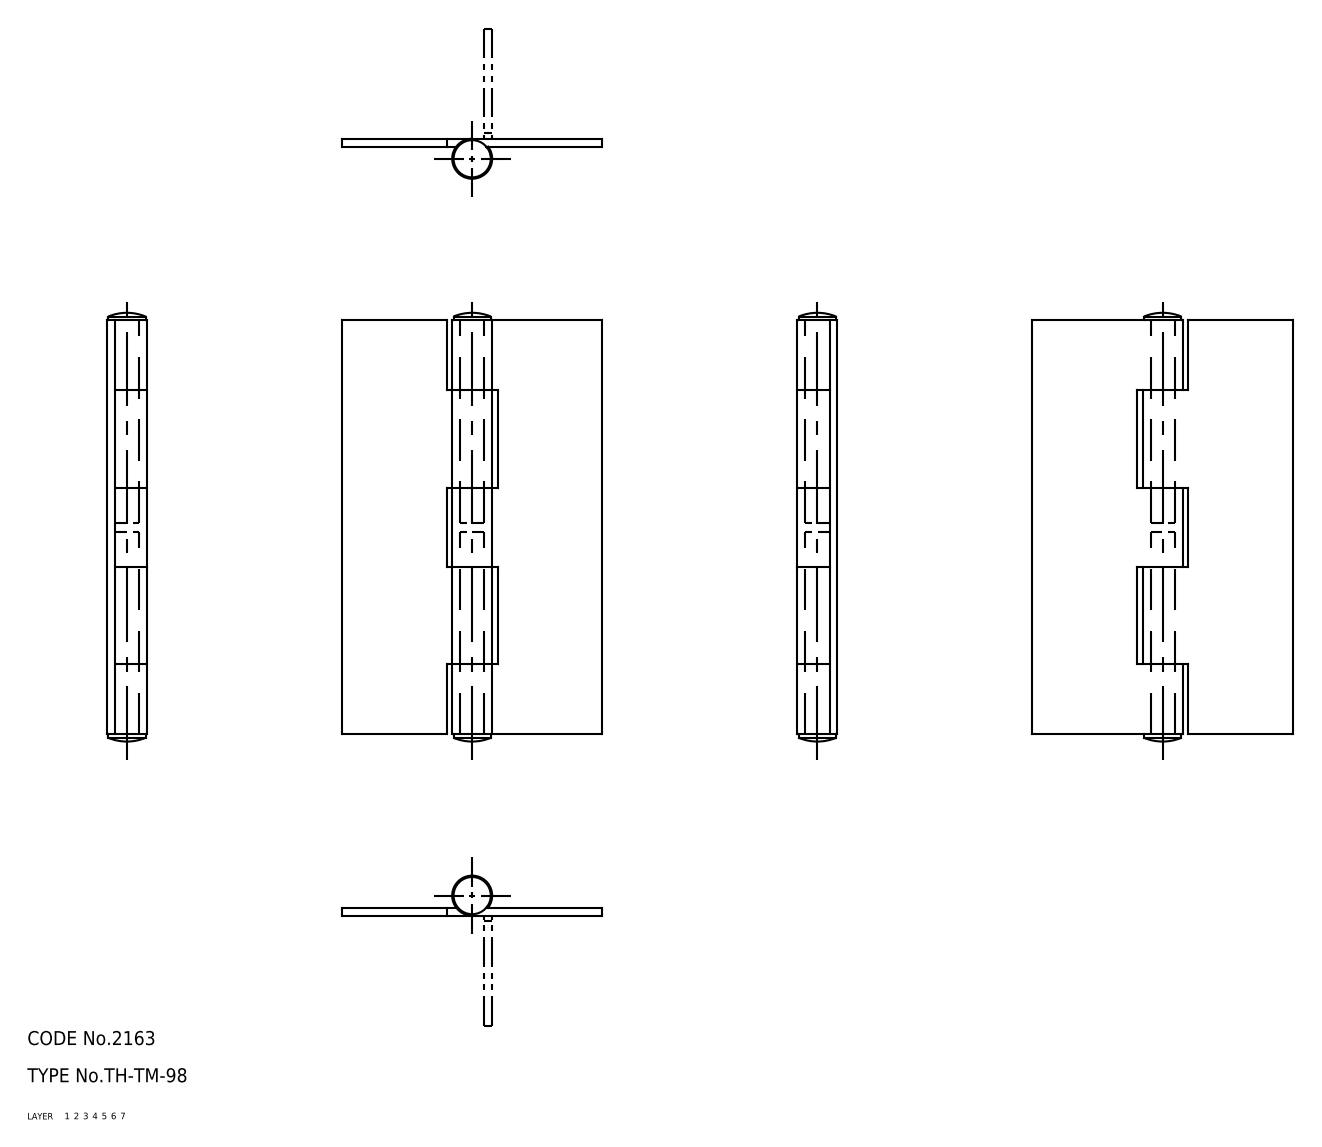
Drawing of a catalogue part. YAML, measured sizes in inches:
part_name: "67111492; 67111505; 67111518; 67111531"
step_written_by: "CADfix (AUTOMOTIVE_DESIGN)"
units: inches
bodies: {solids: 4, faces: 52, planar: 0, cylindrical: 0, other: 52}
overall_size: [3.63, 2.205, 0.339]
volume: 0.757
surface_area: 23.42
